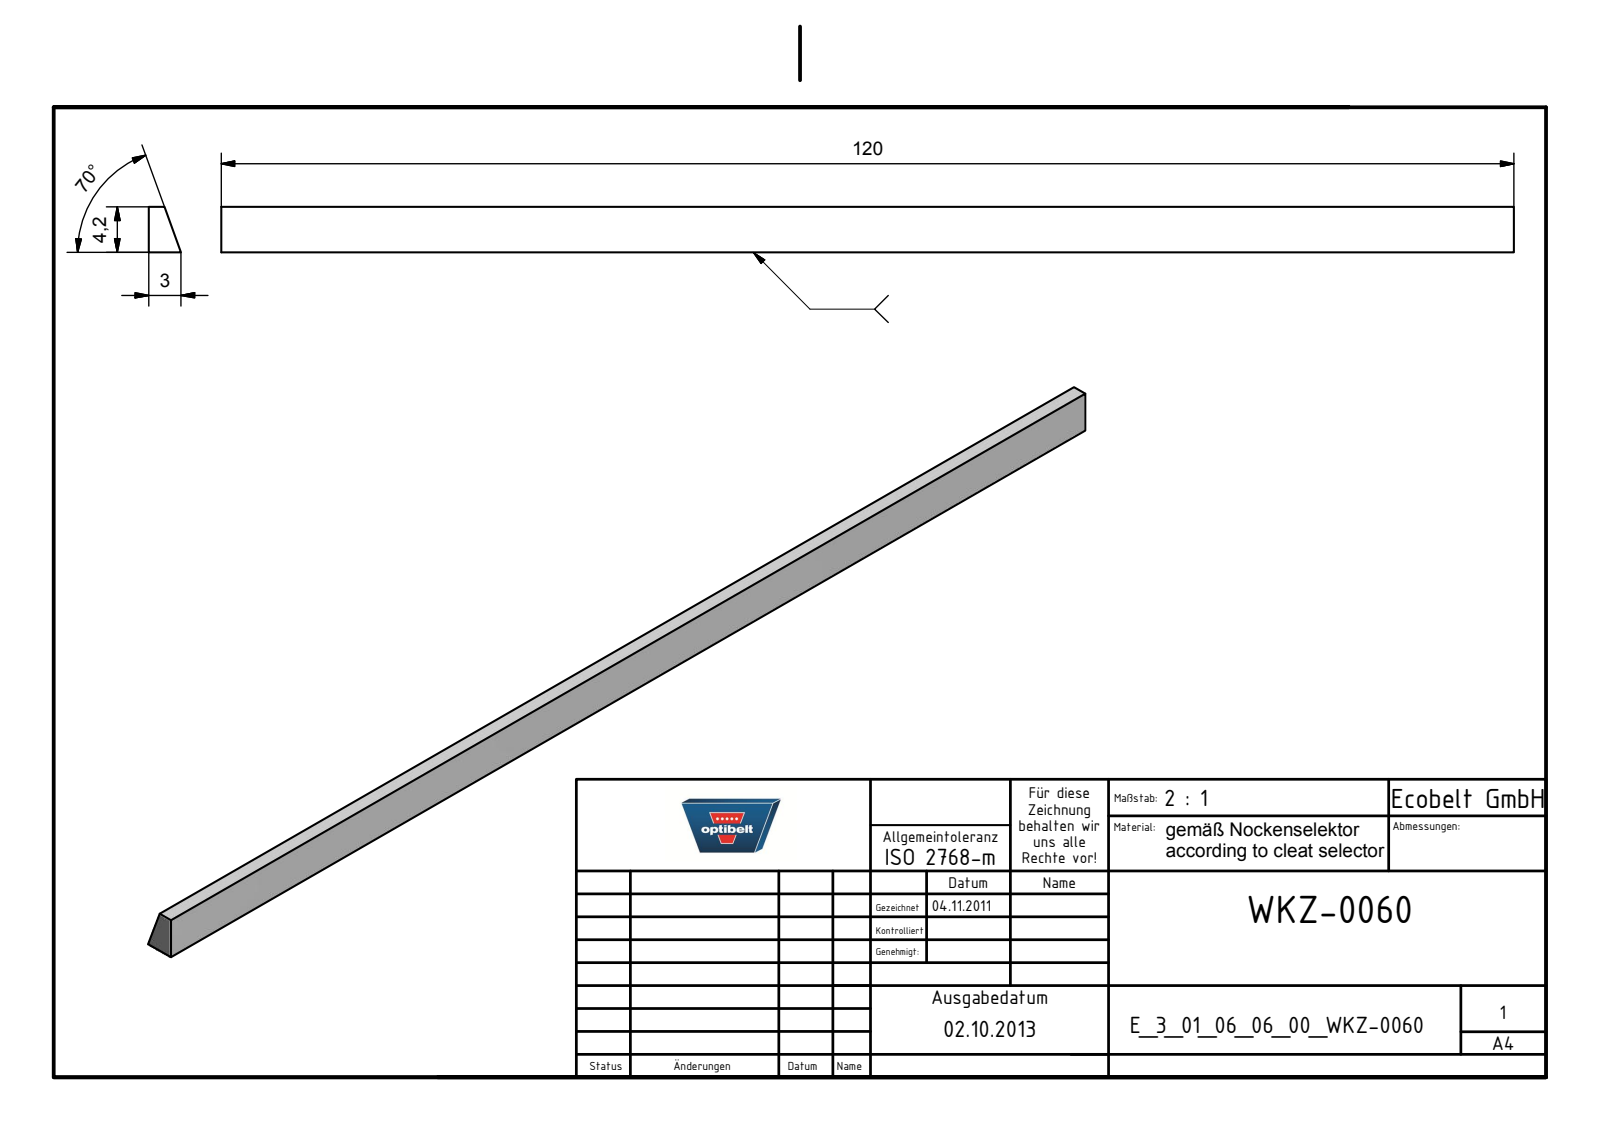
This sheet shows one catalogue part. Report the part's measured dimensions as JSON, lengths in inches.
{"part_name": "E_3_01_06_06_00_WKZ-0060", "step_written_by": "Autodesk Inventor 2025 (AUTOMOTIVE_DESIGN)", "units": "inches", "bodies": {"solids": 1, "faces": 6, "planar": 6, "cylindrical": 0, "other": 0}, "overall_size": [4.724, 0.165, 0.118], "volume_in3": 0.069, "surface_area_in2": 2.474, "face_to_face_distances": [0.165, 4.724]}
